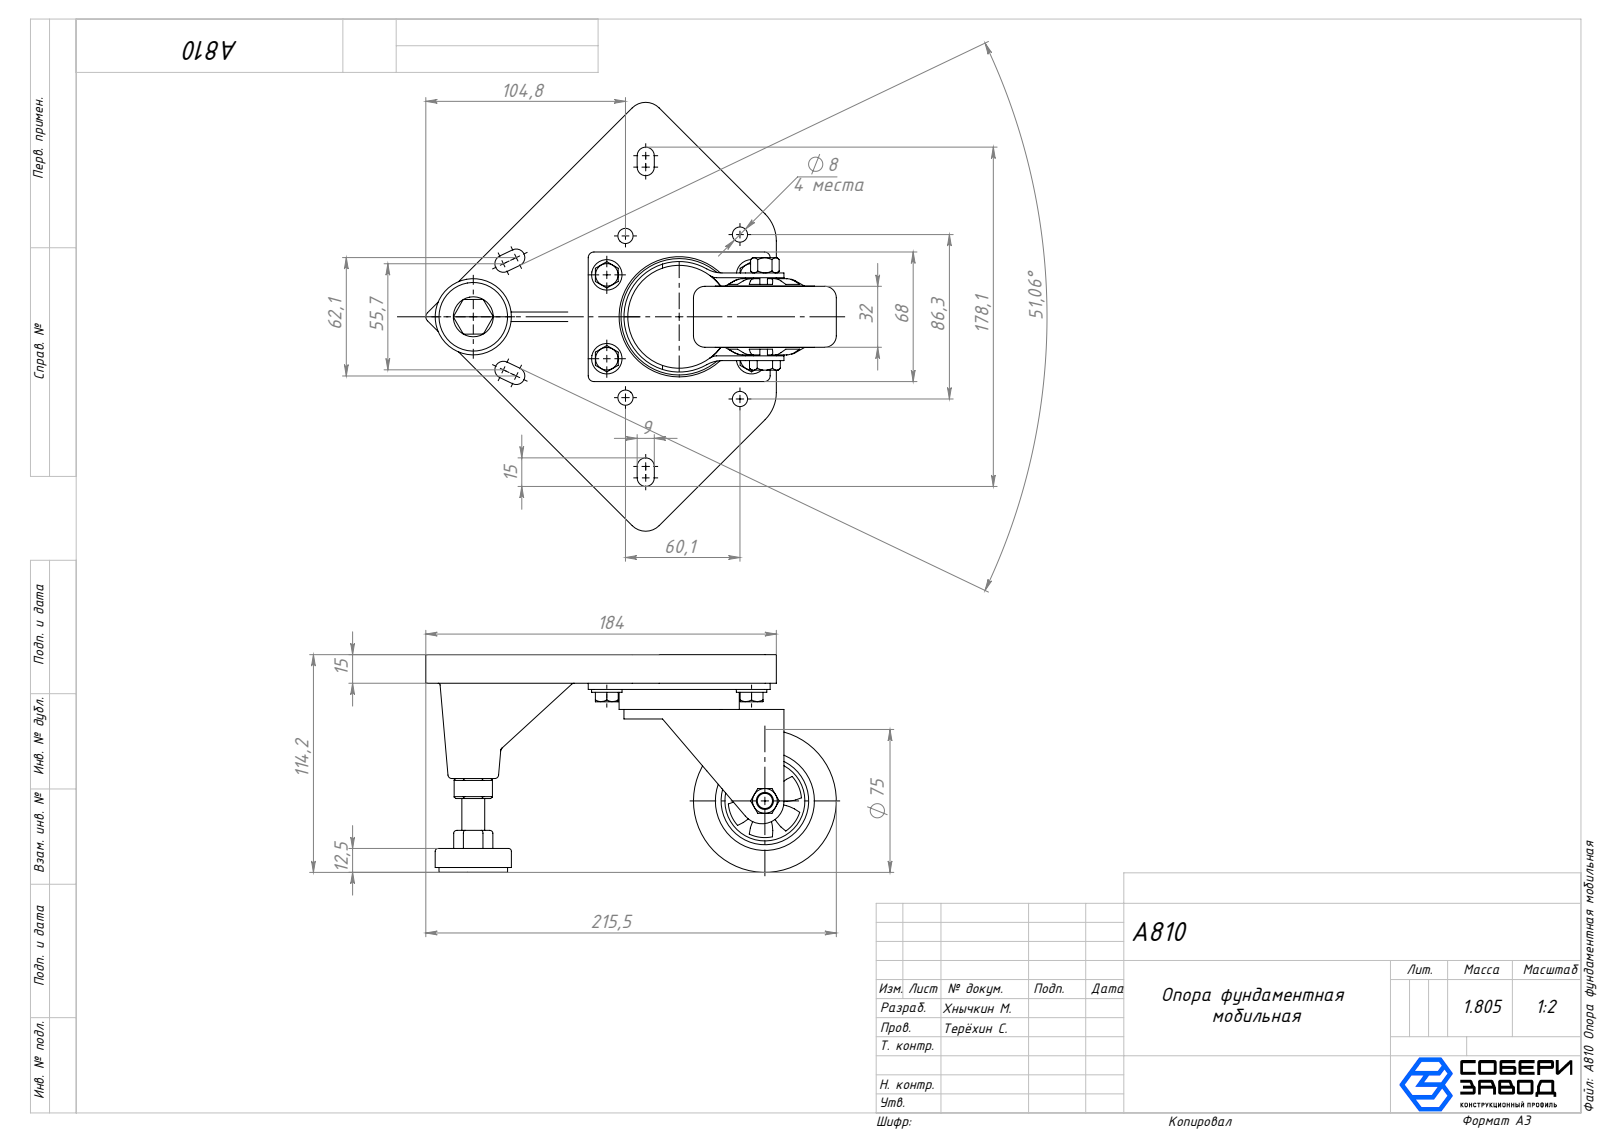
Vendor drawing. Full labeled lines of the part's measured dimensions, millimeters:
Part name (STEP PRODUCT): Вал для ножки_00; Колесо_ось_00; Колесо_колесо_01; Платформа_Болт — копия_00 (+8 more)
STEP written by: SolidWorks 2025 (AUTOMOTIVE_DESIGN)
Units: millimetres
Bodies: 19 solids, 562 faces (198 planar, 223 cylindrical, 141 other)
Overall size (bounding box): 166.5 × 166.5 × 114.25
Volume: 588 620 mm³ · Surface area: 151 609 mm²
Round holes (diameter × count): ⌀8 ×6, ⌀6 ×4, ⌀46 ×2, ⌀10 ×1, ⌀12 ×1, ⌀12.25 ×1, ⌀21 ×1, ⌀61.1 ×1
Round bosses / shafts (diameter × count): ⌀16 ×4, ⌀52 ×2, ⌀75 ×1, ⌀63.1 ×1, ⌀54 ×1, ⌀48 ×1, ⌀40 ×1, ⌀36 ×1
Partial cylindrical surfaces — rounded edges, fillets, slot ends (radius × count): R1 ×34, R20 ×21, R1.5 ×12, R4.5 ×8, R3 ×7, R4 ×6, R3.55 ×2, R5 ×2
Main face-to-face distances: 15, 3.25, 18.25, 6, 9, 12.25, 13.75, 28.75, 22.75, 10.5
Hole centre spacings: 21.99, 22.66, 43.9, 43.91, 44, 50.94, 53.65, 60.11
